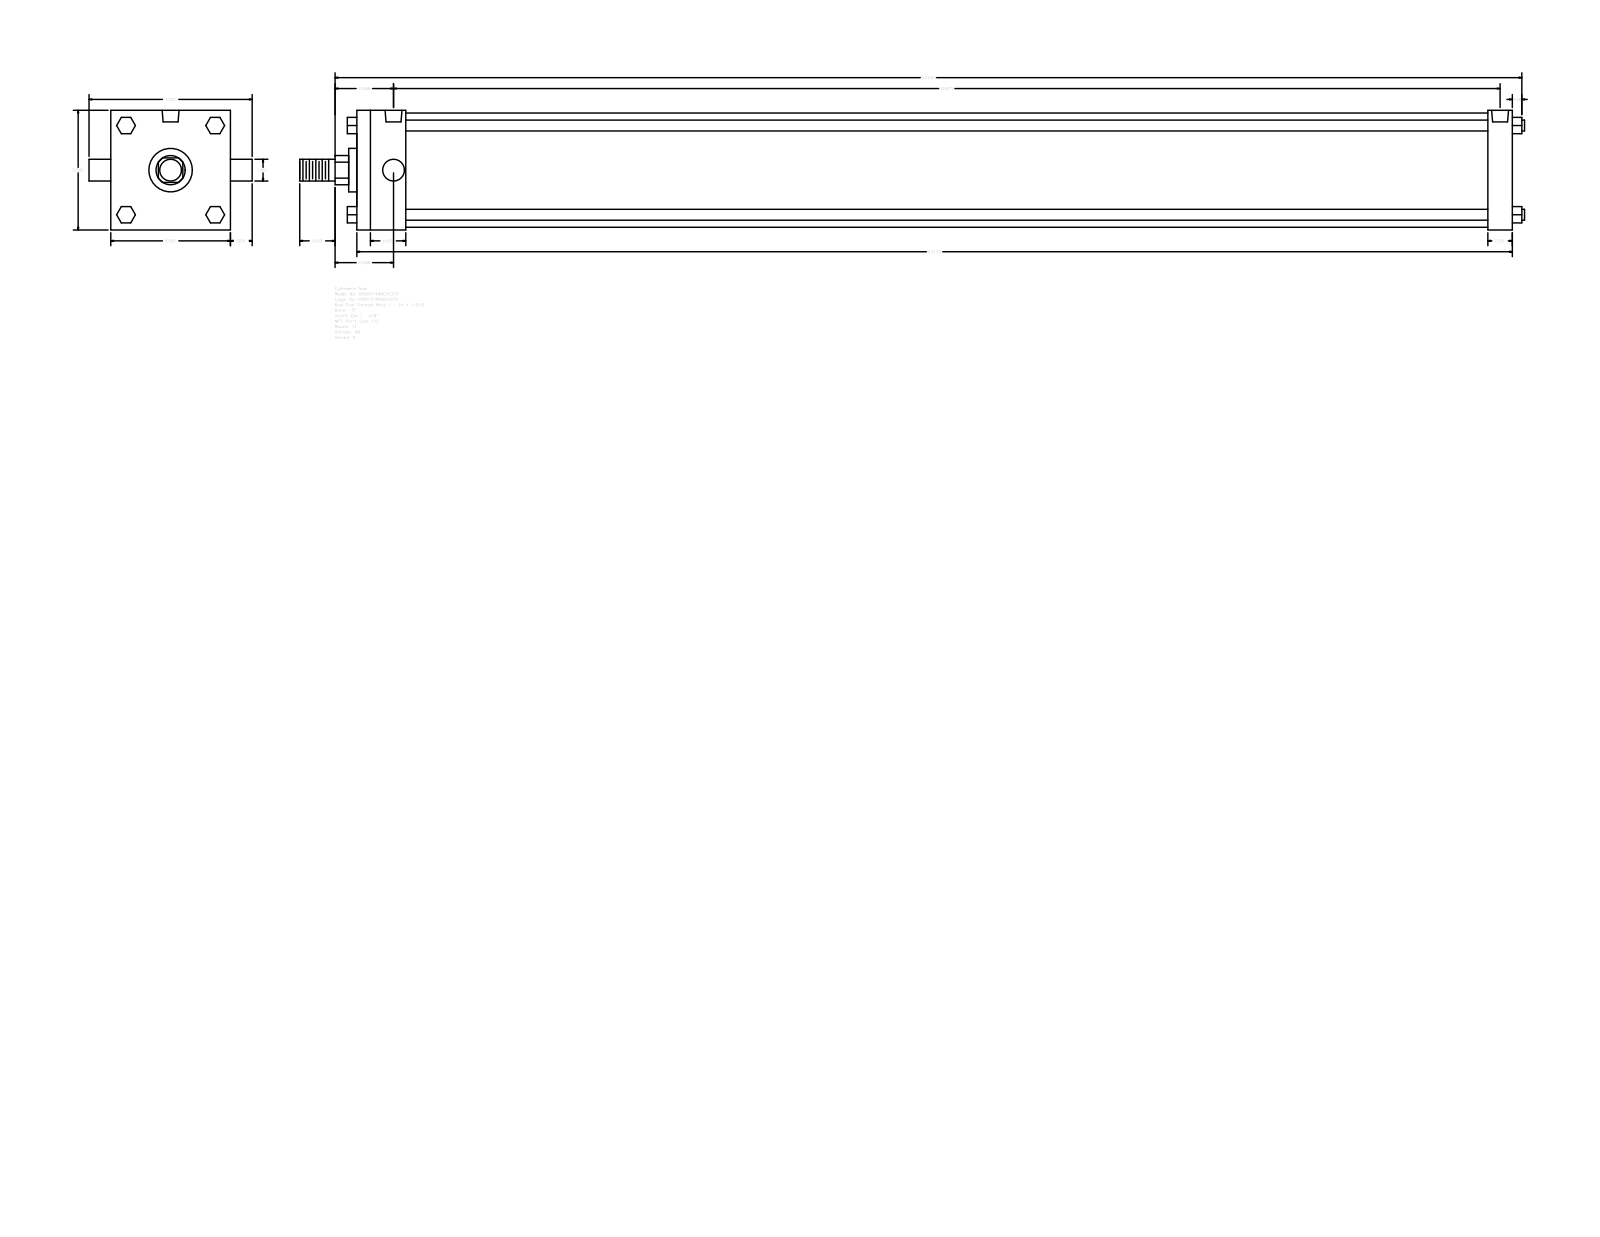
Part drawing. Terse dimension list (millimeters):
name: A_TF__0500_1.375
written by: GSSL Pune (CONFIG_CONTROL_DESIGN)
unit: mm
bodies: 0 solids, 120 faces (92 planar, 28 cylindrical, 0 other)
size: 1430.34 × 190.5 × 139.7
holes: 3× ⌀8.73, 2× ⌀19.77
bosses: 4× ⌀12.7, 2× ⌀25.4, 1× ⌀133.35, 1× ⌀50.8, 1× ⌀34.92
rounds: 1× R17.06
face distances: 139.7, 1349.38, 57.15, 28.58, 1320.8, 1263.65, 1292.23, 19.05, 52.07, 90.18
hole spacings: 2.39, 1289.84, 1287.45, 1292.23
